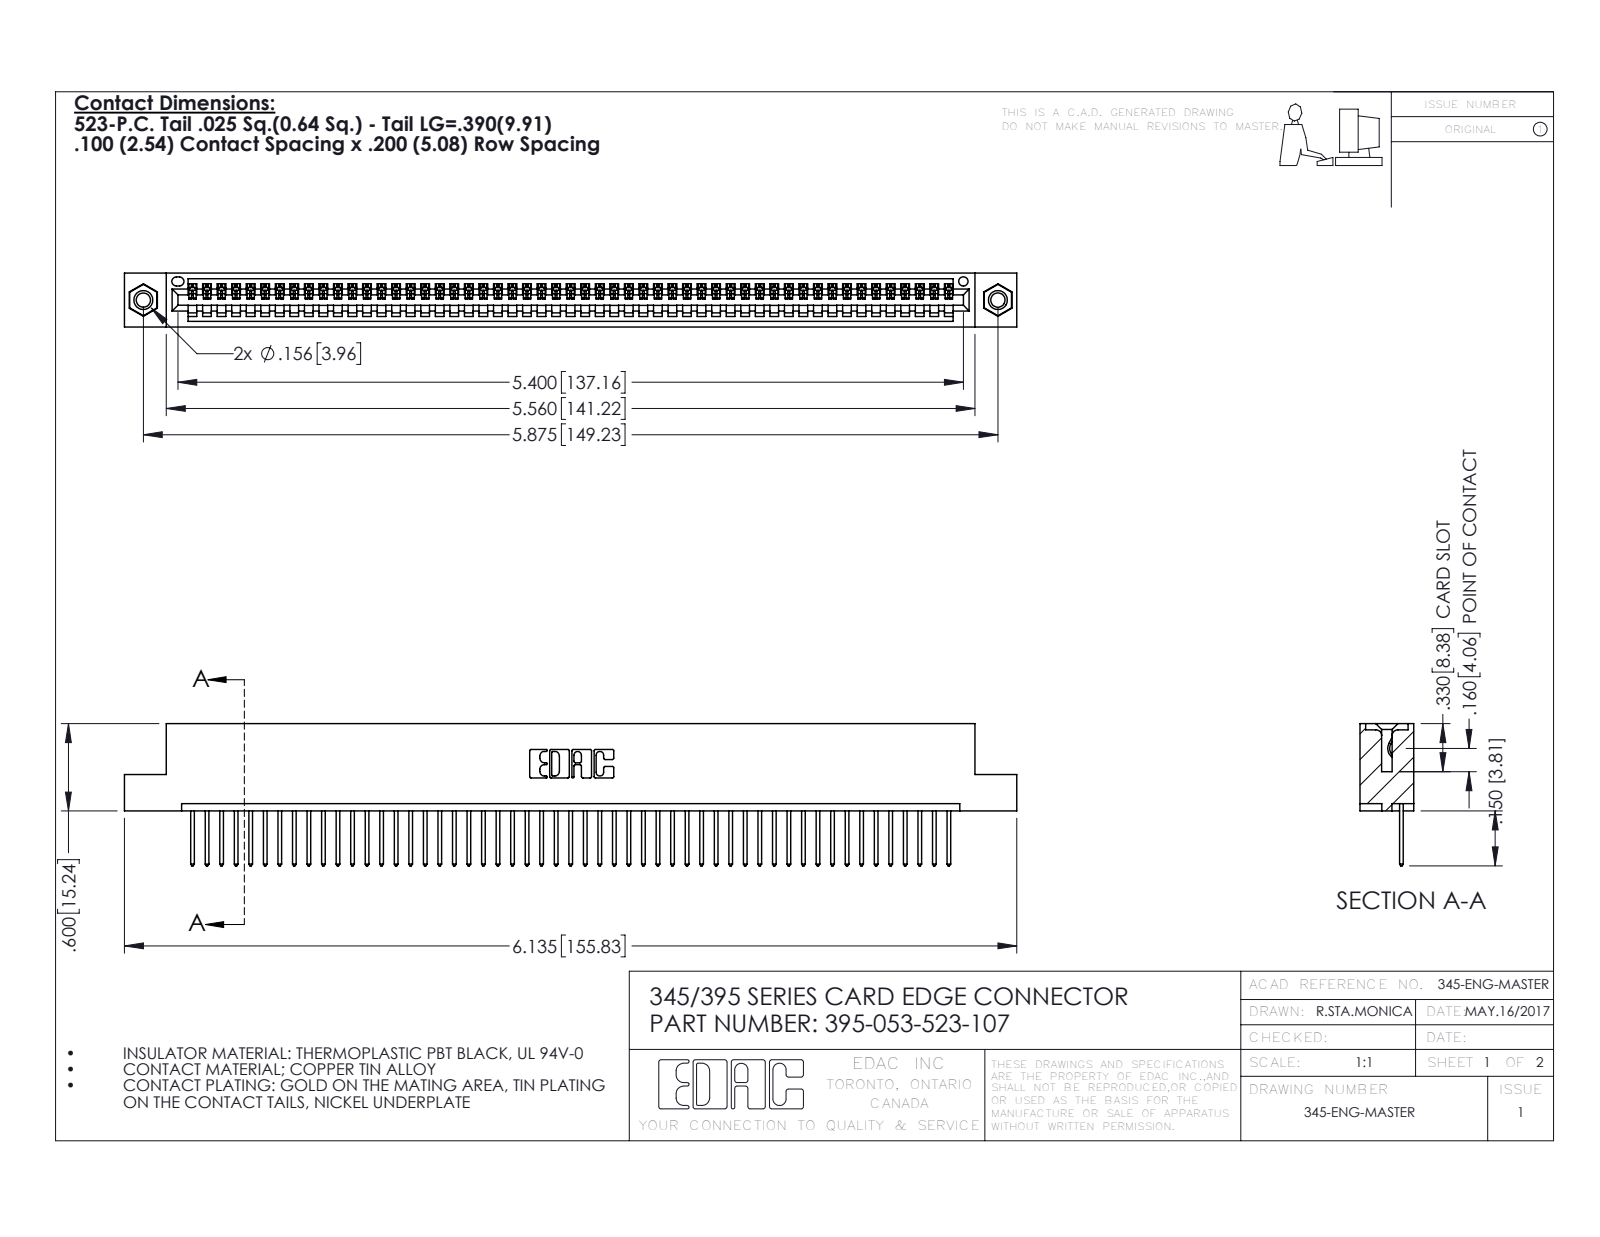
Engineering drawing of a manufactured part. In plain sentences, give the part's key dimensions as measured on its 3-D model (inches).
The part is named "345 Part_Flush Mounting Lugs - 0.156 Dia-TI; 345-292-001_345-293-123; 345-250-001_345-250-005-103; 395-053-523-107". Its 3-D file was written by "SolidWorks 2016 (CONFIG_CONTROL_DESIGN)". It is 56 solids with 3260 faces: 2232 planar, 1012 cylindrical and 16 other. Overall it measures 6.135 by 0.977 by 0.37 inches. Its volume is 0.907 cubic inches and its surface area 30.97 square inches. Round holes: 2 of diameter 0.098, 2 of diameter 0.125, 2 of diameter 0.156, 1 of diameter 0.064. Round bosses or shafts: 2 of diameter 0.155. Partial cylindrical surfaces (rounded edges, fillets, slot ends): 106 of radius 0.006, 106 of radius 0.01, 22 of radius 0.01, 6 of radius 0.007, 6 of radius 0.031, 3 of radius 0.026, 2 of radius 0.031, 2 of radius 0.04. The main face-to-face distances are 0.072, 0.298, 0.37, 0.2, 0.098, 0.272, 0.025, 0.225, 0.149, 0.072. The hole center spacings are 0.27, 5.639, 5.875.
